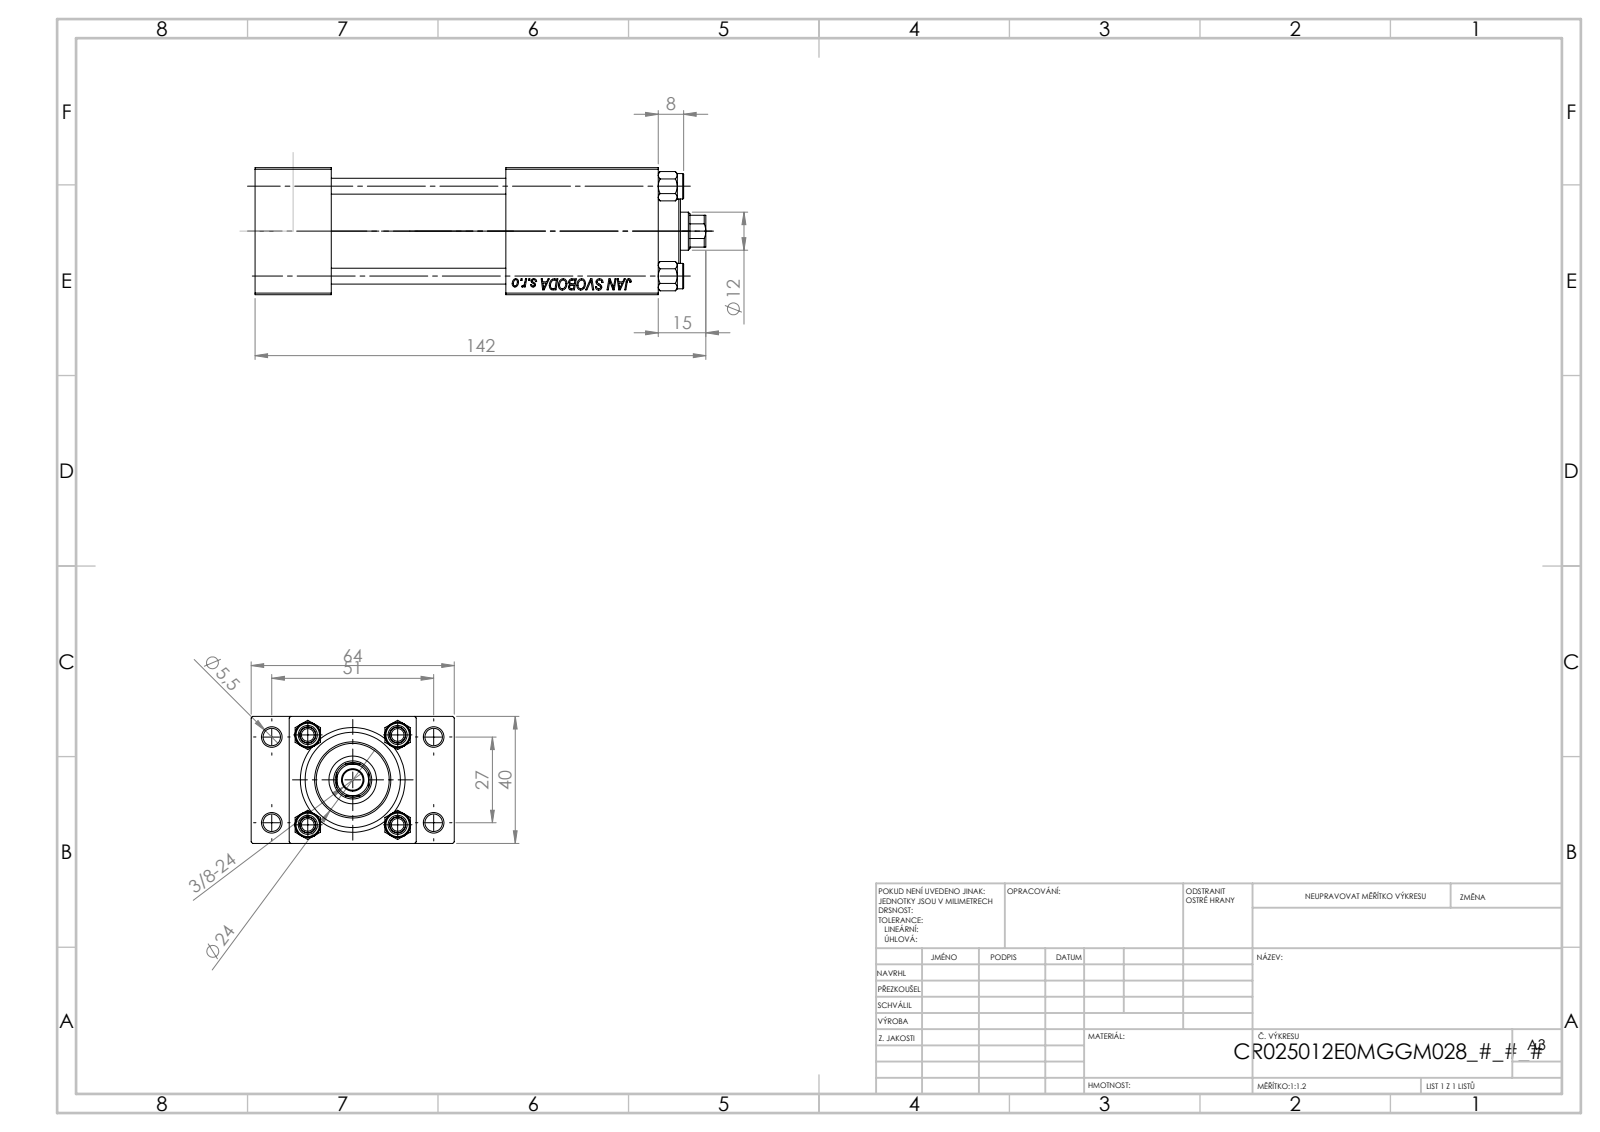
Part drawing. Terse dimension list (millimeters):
name: V215CR_TYCINKA_E; V215CR_VCP_E; V215_VC_A; V215CR_E_Body (+1 more)
written by: SolidWorks 2019 (CONFIG_CONTROL_DESIGN)
unit: mm
bodies: 11 solids, 1136 faces (497 planar, 87 cylindrical, 552 other)
size: 142 × 64 × 40
volume: 167 559 mm³; area: 64 316 mm²
holes: 4× ⌀5, 4× ⌀5.5, 3× ⌀20, 2× ⌀7, 2× ⌀13.16, 1× ⌀6.5, 1× ⌀12, 1× ⌀15, 1× ⌀25, 1× ⌀30
bosses: 4× ⌀8, 1× ⌀31, 1× ⌀24
rounds: 1× R5.5
face distances: 40, 24, 12, 52, 55, 127, 103, 98.3, 74.3, 28.7
hole spacings: 11.37, 20.01, 28.3, 28.85, 29.89, 39.66, 48.34, 27
